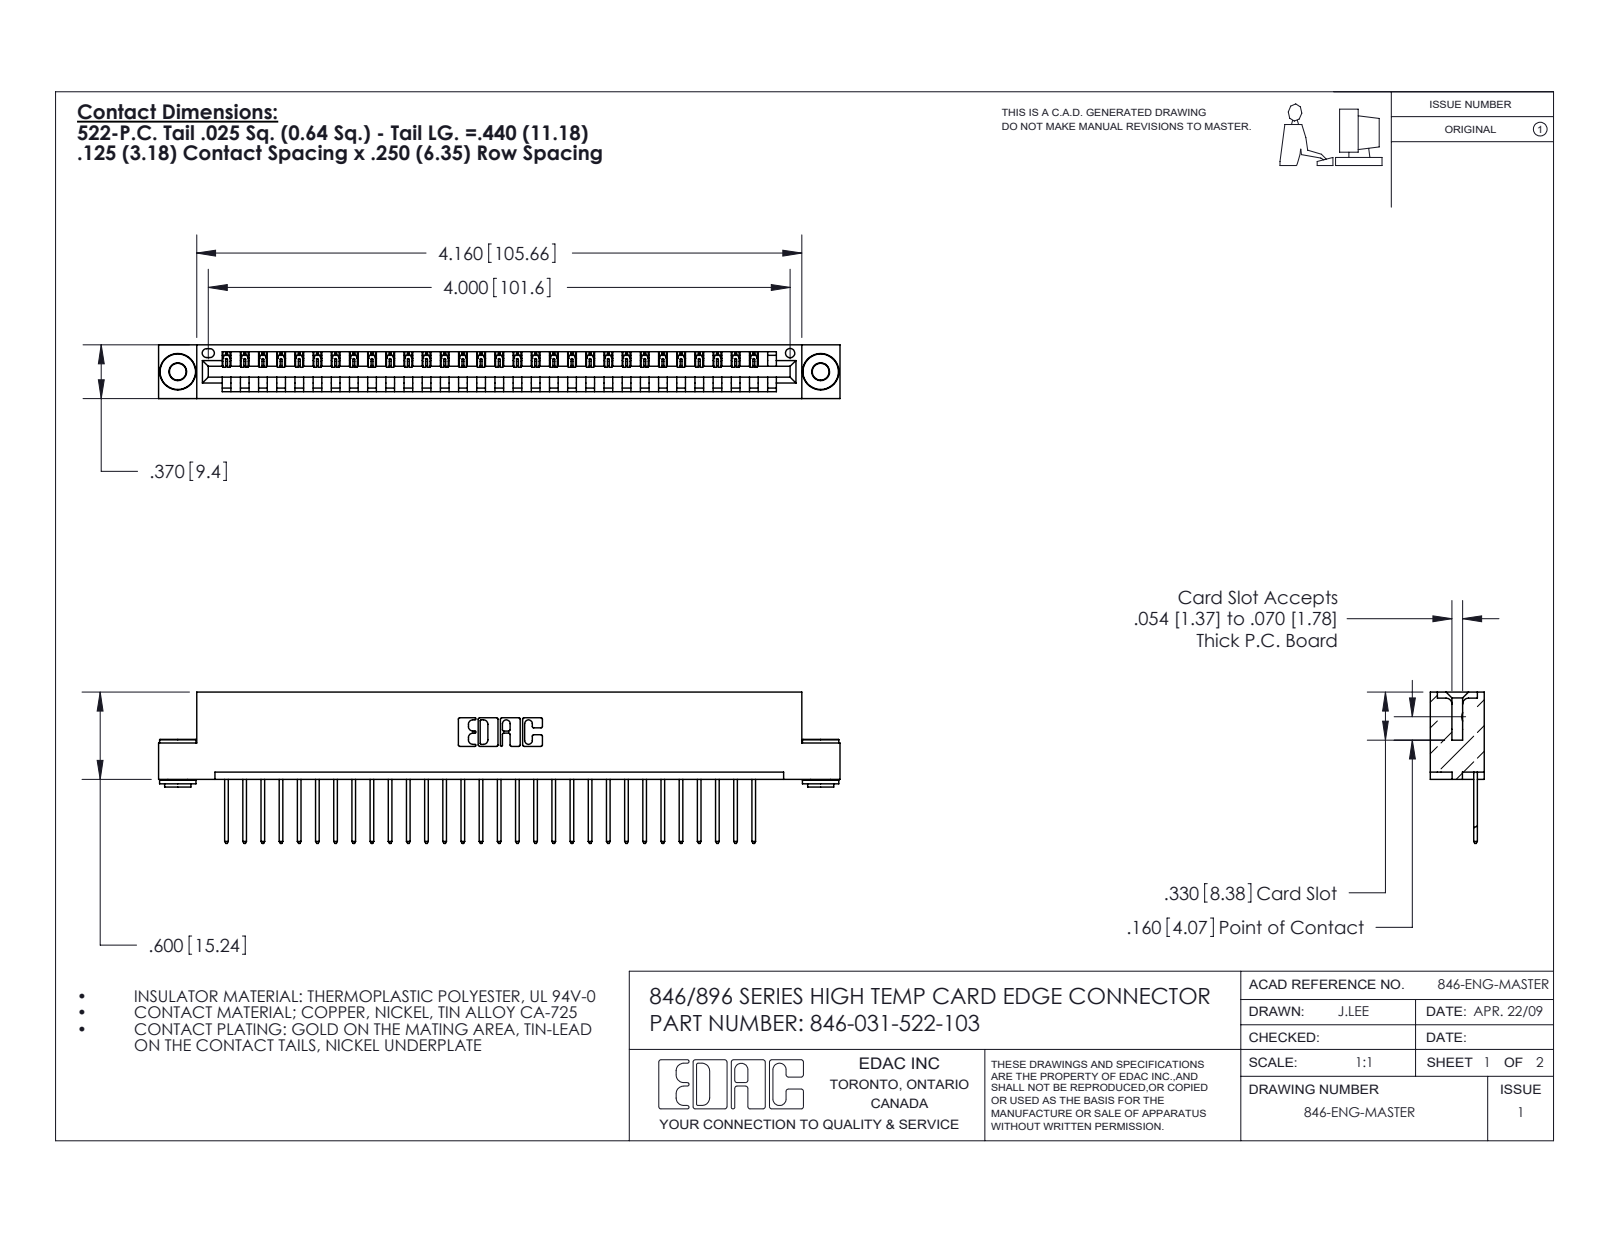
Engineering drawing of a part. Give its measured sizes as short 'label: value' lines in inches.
name: 346-031-522-103; 346 Part_Flush Mounting Lugs - 0.156 Dia-TH; 345-250-002_345-250-002-102; 345-292-001_345-293-122
written by: SolidWorks 2016 (CONFIG_CONTROL_DESIGN)
unit: in
bodies: 34 solids, 1958 faces (1326 planar, 624 cylindrical, 8 other)
size: 4.685 × 1.04 × 0.37
volume: 0.692 in³; area: 22.3 in²
holes: 2× ⌀0.116, 2× ⌀0.156, 1× ⌀0.064
bosses: 2× ⌀0.25, 2× ⌀0.18, 2× ⌀0.136
rounds: 62× R0.006, 62× R0.01, 22× R0.01, 6× R0.007, 6× R0.031, 3× R0.026, 2× R0.031, 2× R0.04
face distances: 0.048, 0.322, 0.25, 0.37, 0.025, 0.072, 0.298, 0.148, 0.222, 0.1
hole spacings: 0.246, 4.212, 4.42
